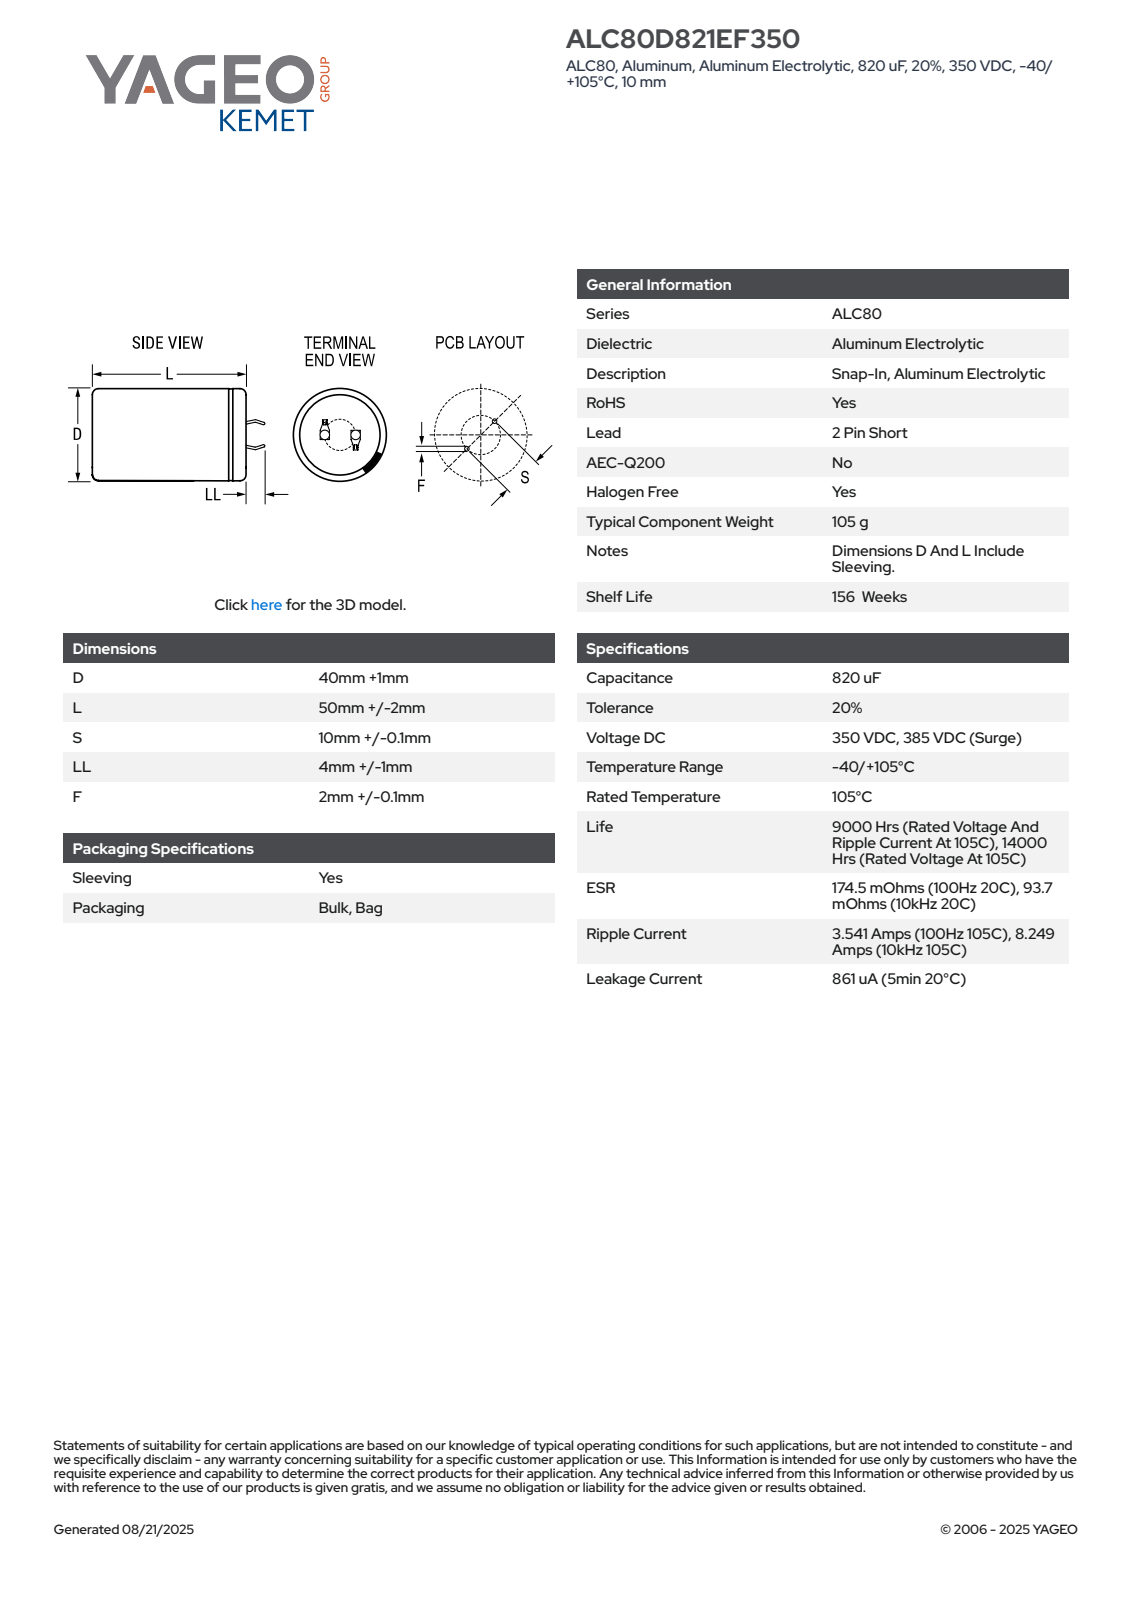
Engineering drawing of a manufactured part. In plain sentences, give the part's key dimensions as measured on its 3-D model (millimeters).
The part is named "CARS_K2P_40X50_D41L52S10LL5F2.1". Its 3-D file was written by "SolidWorks 2014 (AUTOMOTIVE_DESIGN)". It is 1 solid with 100 faces: 52 planar, 9 cylindrical and 39 other. Overall it measures 56.99 by 41 by 41 millimeters. Its volume is 67 867 cubic millimeters and its surface area 9 310 square millimeters. Round holes: 1 of diameter 36.28. Round bosses or shafts: 1 of diameter 41. Partial cylindrical surfaces (rounded edges, fillets, slot ends): 1 of radius 20.49. The main face-to-face distances are 51.99, 52.49, 0.5, 7.08, 0.6, 0.59, 7.6, 0.75, 1.35, 7.68.
